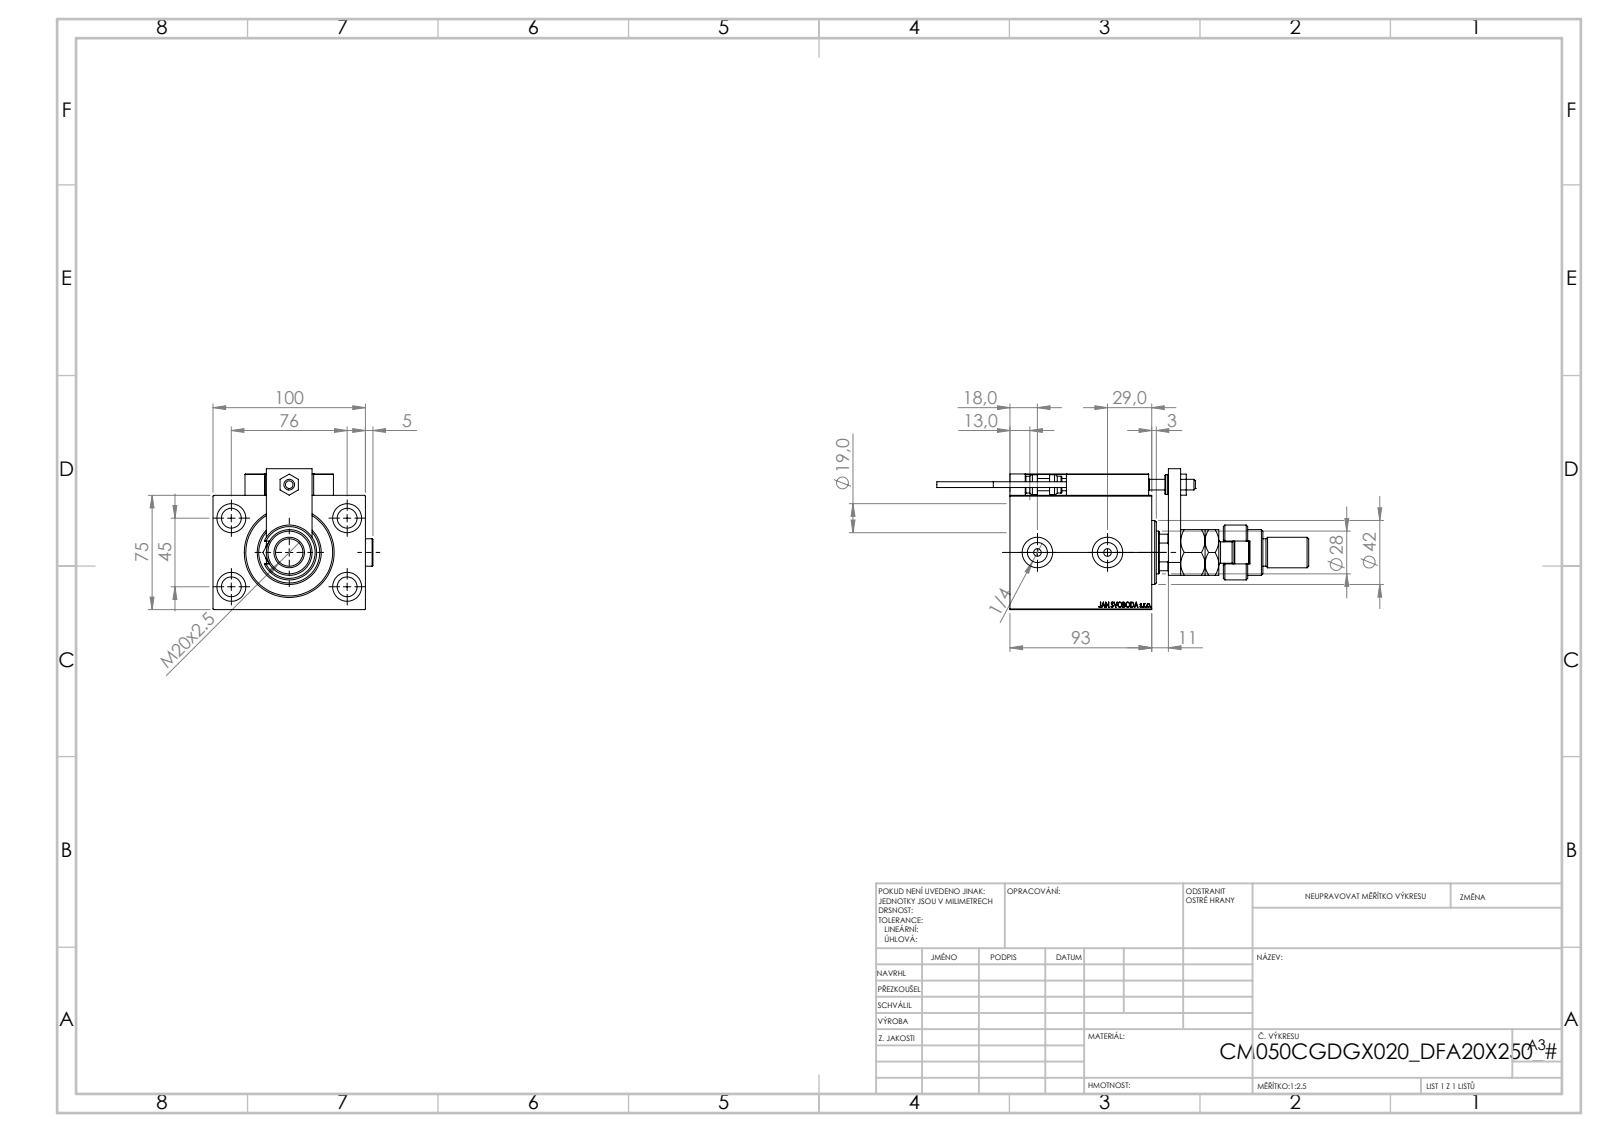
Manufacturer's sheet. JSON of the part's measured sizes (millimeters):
{"part_name": "NUT_D12; KONCOVKA; ALLEN BOLT D8; MFA (+7 more)", "step_written_by": "SolidWorks 2019 (CONFIG_CONTROL_DESIGN)", "units": "millimeters", "bodies": {"solids": 27, "faces": 1422, "planar": 623, "cylindrical": 217, "other": 582}, "overall_size": [244, 104.9, 92.5], "volume_mm3": 717130, "surface_area_mm2": 139000, "round_holes": [[8, 5], [3.2, 4], [4, 4], [5, 4], [13, 4], [19, 4], [20, 3], [13.16, 2], [7, 1], [18.5, 1], [28, 1], [31.5, 1]], "round_bosses_or_shafts": [[18, 3], [5, 2], [3.8, 2], [42, 1], [36, 1], [30, 1], [22, 1], [14, 1]], "partial_cylinders_radius": [[0.3, 30], [3, 2], [7.5, 1], [12, 1], [13.5, 1]], "face_to_face_distances": [75, 100, 93, 51, 42, 8, 70, 14, 10, 13], "hole_center_spacings": [44.16, 11.37, 20, 29.59, 29.69, 36.06, 42.19, 43.91]}
